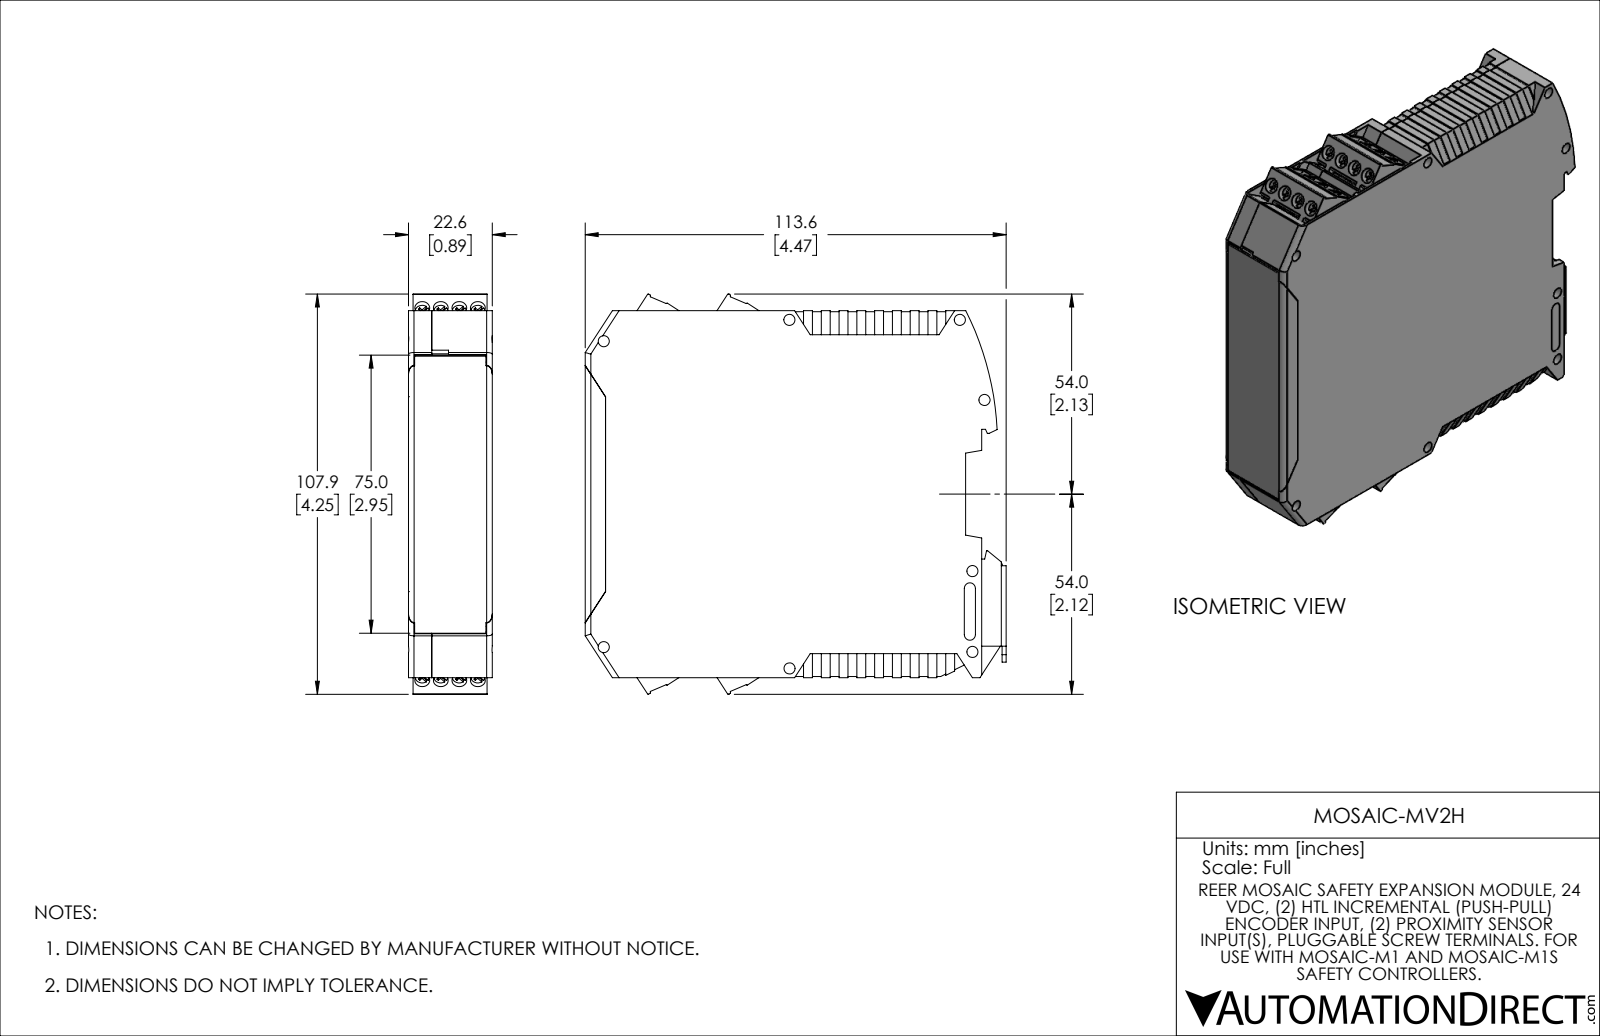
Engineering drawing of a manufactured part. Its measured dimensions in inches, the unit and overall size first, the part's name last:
Units: inches
Overall size (bounding box): 4.472 × 4.25 × 0.89
Round holes (diameter × count): ⌀0.055 ×18, ⌀0.11 ×16, ⌀0.157 ×16, ⌀0.118 ×14, ⌀0.063 ×1
Round bosses / shafts (diameter × count): ⌀0.149 ×16, ⌀0.177 ×1, ⌀0.11 ×1, ⌀0.053 ×1
Partial cylindrical surfaces — rounded edges, fillets, slot ends (radius × count): R0.012 ×33, R0.114 ×16, R0.008 ×12, R0.03 ×12, R0.059 ×8, R0.031 ×6, R0.098 ×5, R0.024 ×4
Main face-to-face distances: 0.049, 0.841, 0.89, 0.791, 0.039, 0.248, 0.047, 0.199, 0.593, 0.642
Hole centre spacings: 0.197, 0.394, 0.591, 0.503, 0.504, 0.74, 0.74, 0.463
Volume: 3.484 in³ · Surface area: 117.5 in²
Bodies: 9 solids, 1954 faces (1569 planar, 379 cylindrical, 6 other)
Part name (STEP PRODUCT): MOSAIC-MV2H
STEP written by: SolidWorks 2021 (AUTOMOTIVE_DESIGN)
